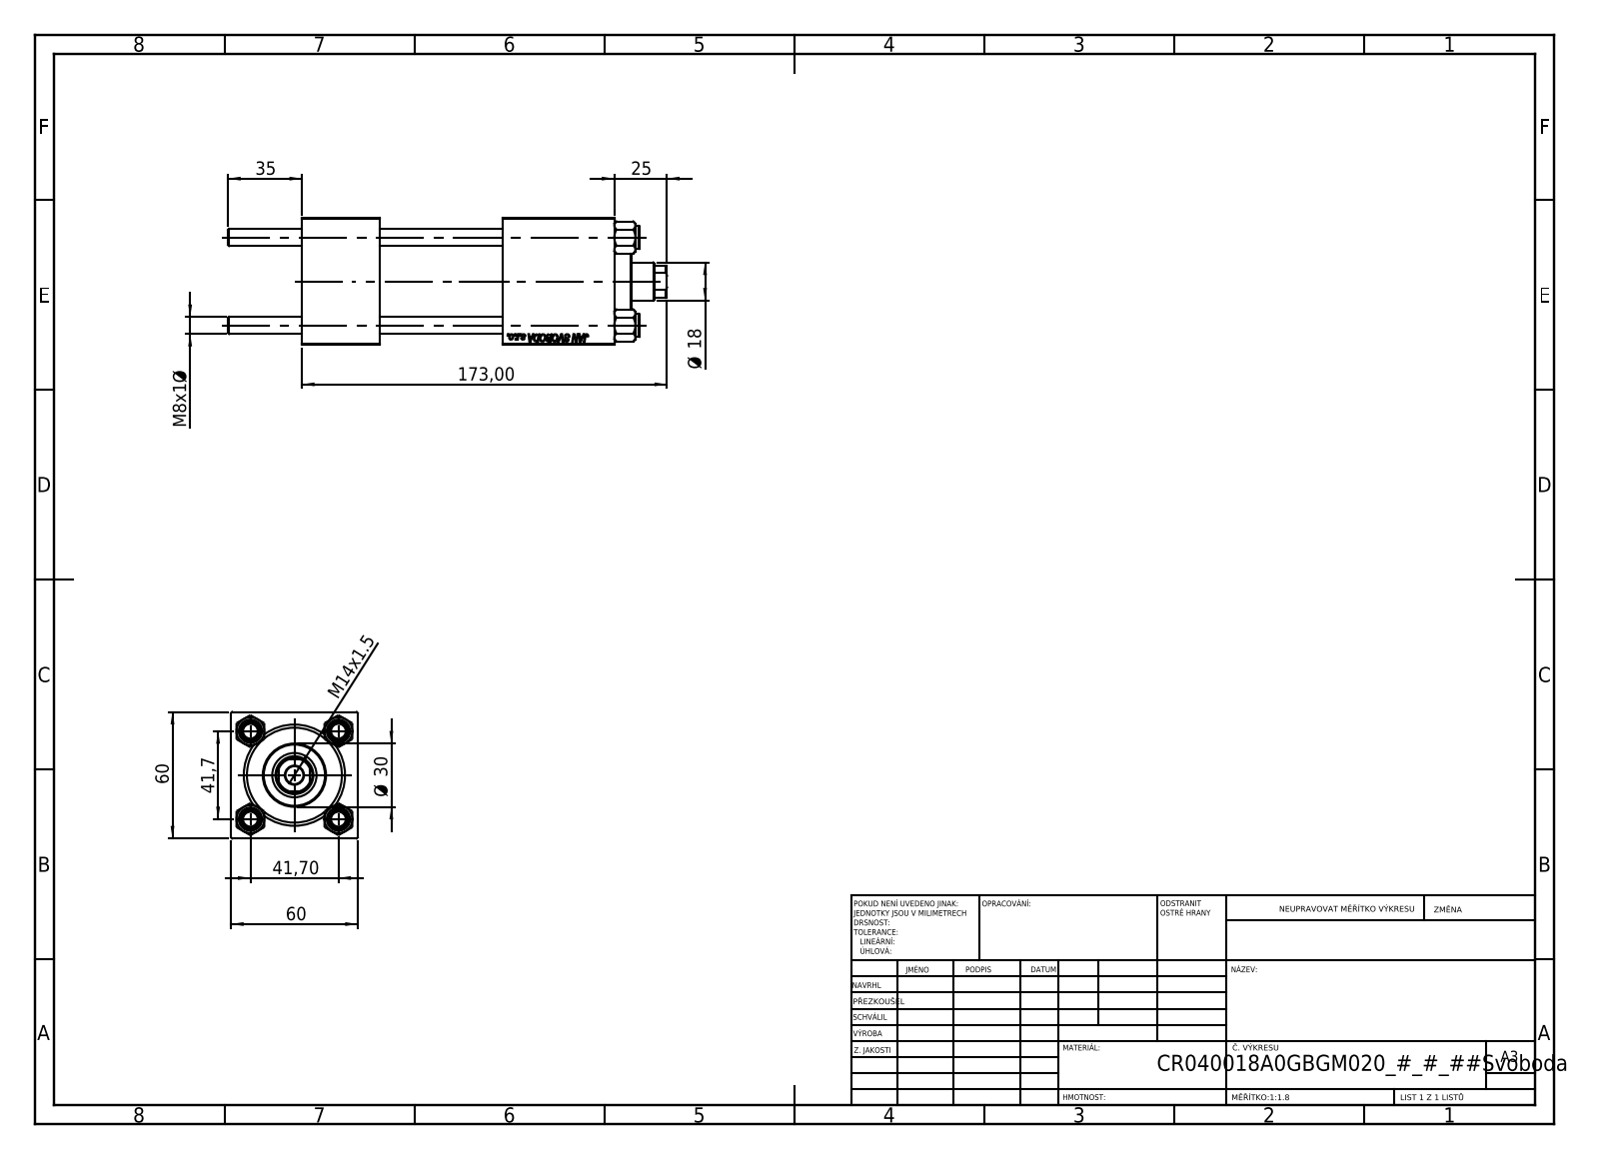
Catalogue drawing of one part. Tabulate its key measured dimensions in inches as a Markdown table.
| quantity | value |
| --- | --- |
| part name | V215_VC_A; CR025_012_A_0_G_A_G_M_020_+#_##_TYCINKA; V215CR_BODY_A; NUT_M5 (+1 more) |
| STEP written by | SolidWorks 2019 (CONFIG_CONTROL_DESIGN) |
| units | inches |
| bodies | 11 solids, 1134 faces (520 planar, 78 cylindrical, 536 other) |
| overall size | 8.189 × 2.362 × 2.362 |
| volume | 25.26 in³ |
| surface area | 176.7 in² |
| round holes (diameter × count) | 0.315 × 4, 0.276 × 2, 0.656 × 2, 0.945 × 2, 0.335 × 1, 0.709 × 1, 0.827 × 1, 1.22 × 1, 1.575 × 1, 1.772 × 1 |
| round bosses / shafts (diameter × count) | 0.433 × 4, 1.811 × 1, 1.181 × 1 |
| partial cylindrical surfaces (radius × count) | 0.335 × 1 |
| main face-to-face distances | 2.362, 1.457, 5.827, 4.37, 2.283, 2.087, 3.74, 4.697, 3.24, 0.957 |
| hole center spacings | 1.161, 1.642, 2.322, 3.642 |
